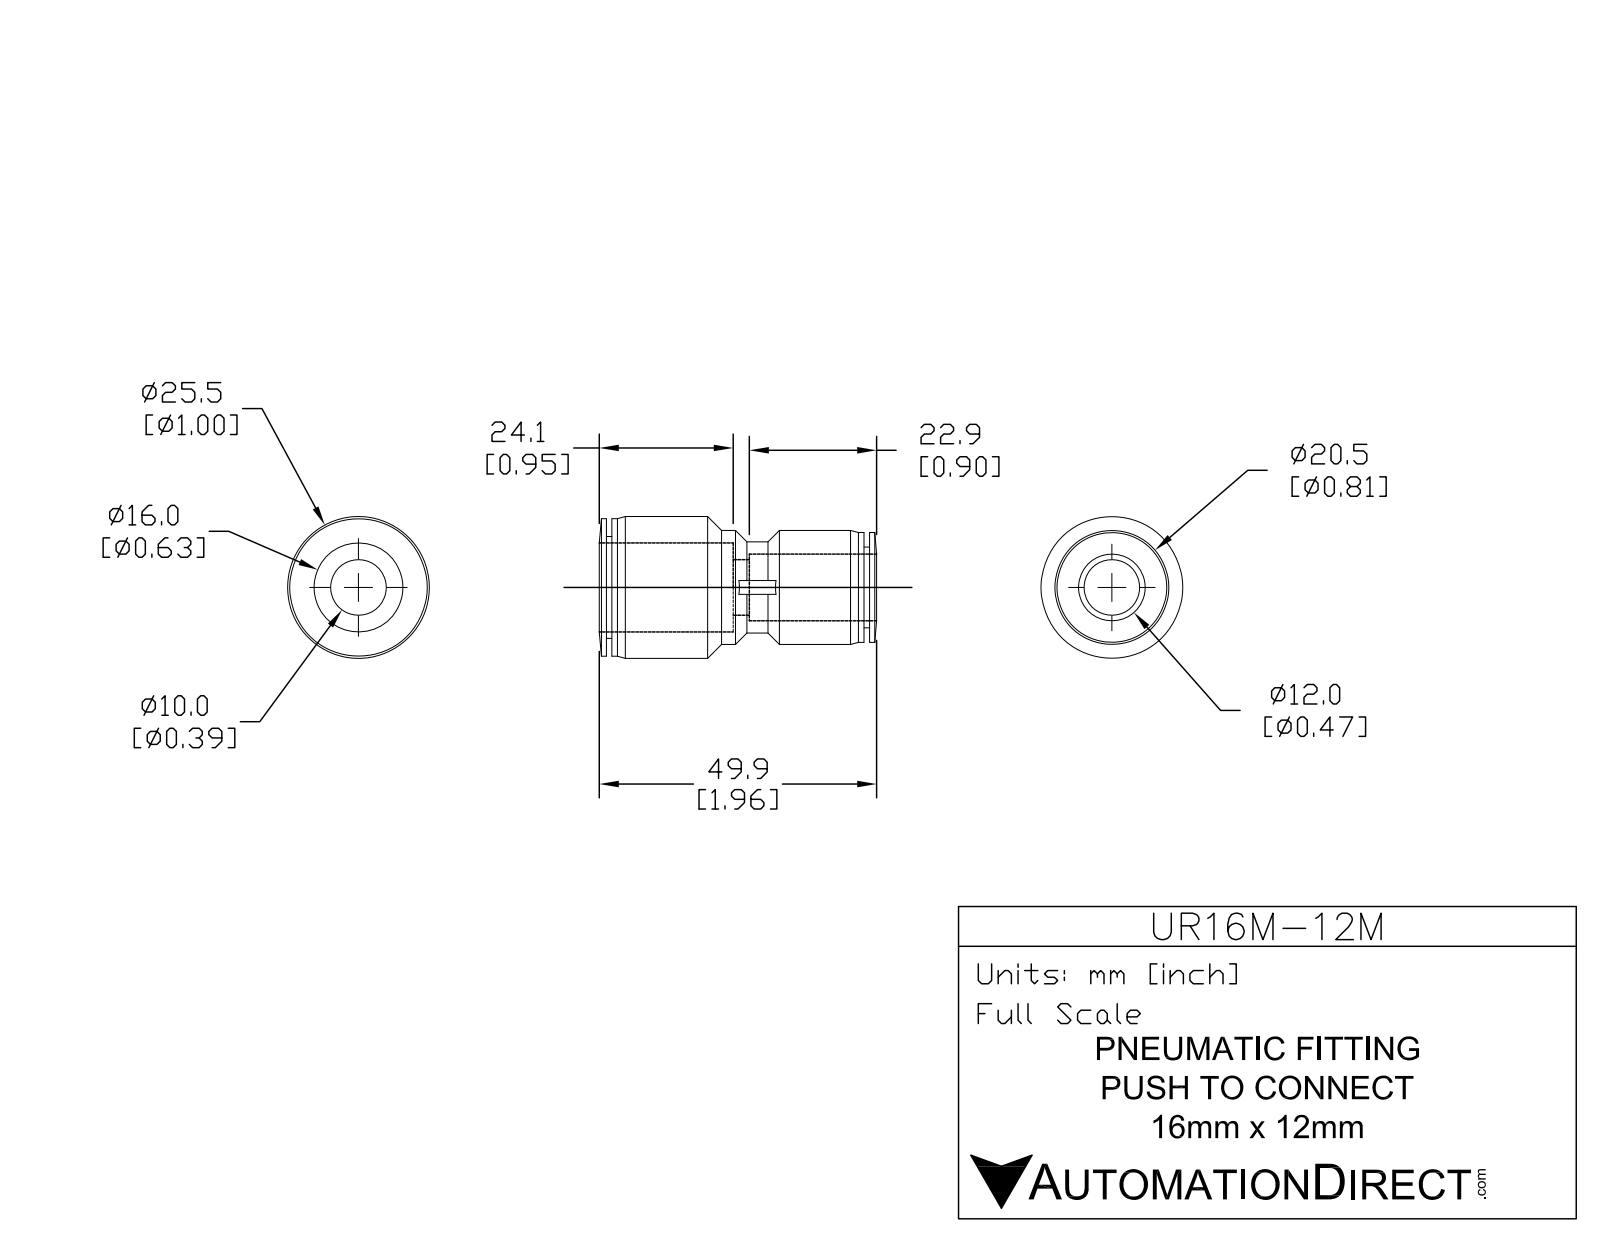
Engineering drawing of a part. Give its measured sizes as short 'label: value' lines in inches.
name: UR16M-12M
written by: SolidWorks 2015 (CONFIG_CONTROL_DESIGN)
unit: in
bodies: 1 solid, 52 faces (12 planar, 26 cylindrical, 14 other)
size: 1.965 × 1.004 × 1.004
volume: 0.684 in³; area: 10.96 in²
holes: 1× ⌀0.394, 1× ⌀0.472, 1× ⌀0.63
bosses: 1× ⌀1.004, 1× ⌀0.974, 1× ⌀0.807, 1× ⌀0.777, 1× ⌀0.722, 1× ⌀0.646, 1× ⌀0.572
face distances: 0.039, 1.825, 1.865, 1.786, 0.899, 0.859, 0.926, 0.966, 1.013, 0.974
